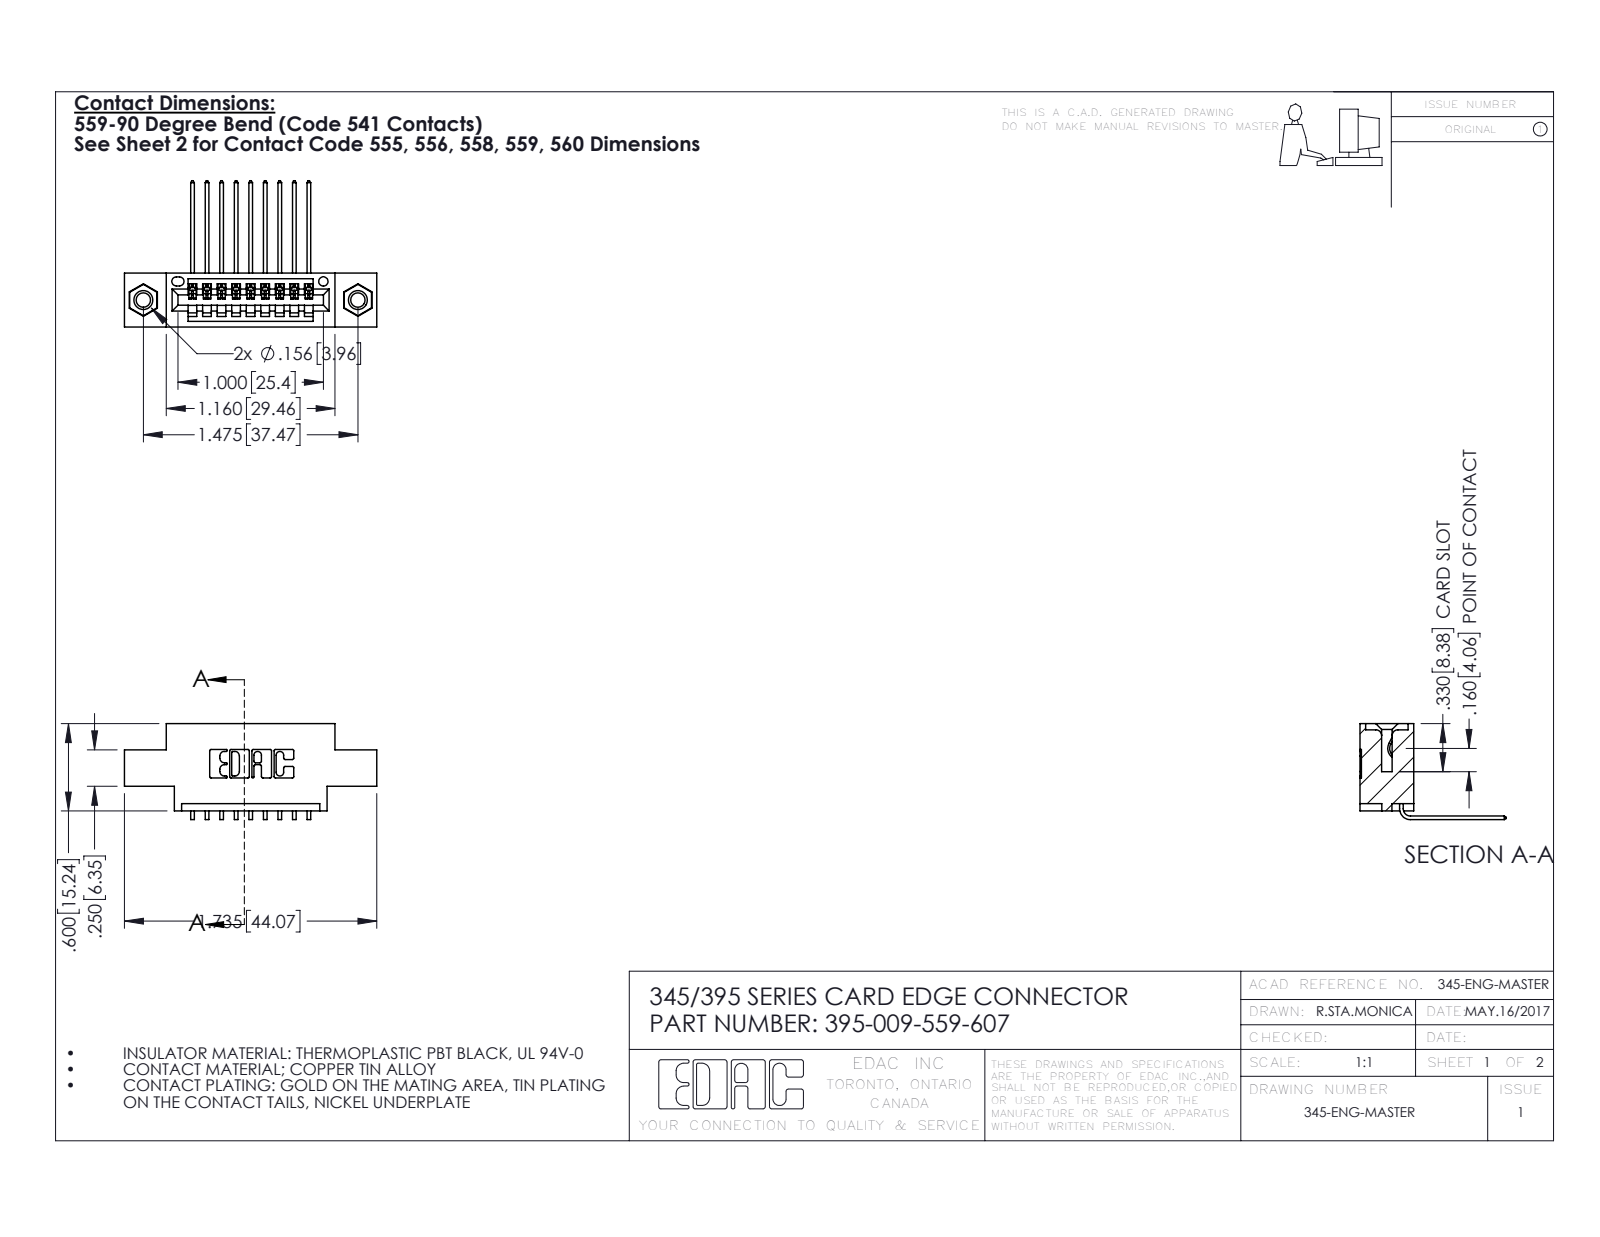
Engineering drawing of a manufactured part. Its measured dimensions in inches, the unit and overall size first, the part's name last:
Units: inches
Overall size (bounding box): 1.735 × 1.005 × 0.659
Round holes (diameter × count): ⌀0.098 ×2, ⌀0.125 ×2, ⌀0.156 ×2, ⌀0.064 ×1
Round bosses / shafts (diameter × count): ⌀0.155 ×2
Partial cylindrical surfaces — rounded edges, fillets, slot ends (radius × count): R0.01 ×22, R0.006 ×18, R0.007 ×6, R0.031 ×6, R0.026 ×3, R0.031 ×2, R0.04 ×2, R0.014 ×1
Main face-to-face distances: 0.37, 0.2, 0.072, 0.298, 0.1, 0.098, 0.272, 0.025, 0.3, 0.6
Hole centre spacings: 0.27, 1.244, 1.475
Volume: 0.233 in³ · Surface area: 7.69 in²
Bodies: 12 solids, 730 faces (494 planar, 220 cylindrical, 16 other)
Part name (STEP PRODUCT): 395-009-559-607; 345-250-001_345-250-005-103; 345-292-001_558 559 Tail - 1; 345 Part_0.170 Offset - 0.156 Dia-TI
STEP written by: SolidWorks 2016 (CONFIG_CONTROL_DESIGN)
